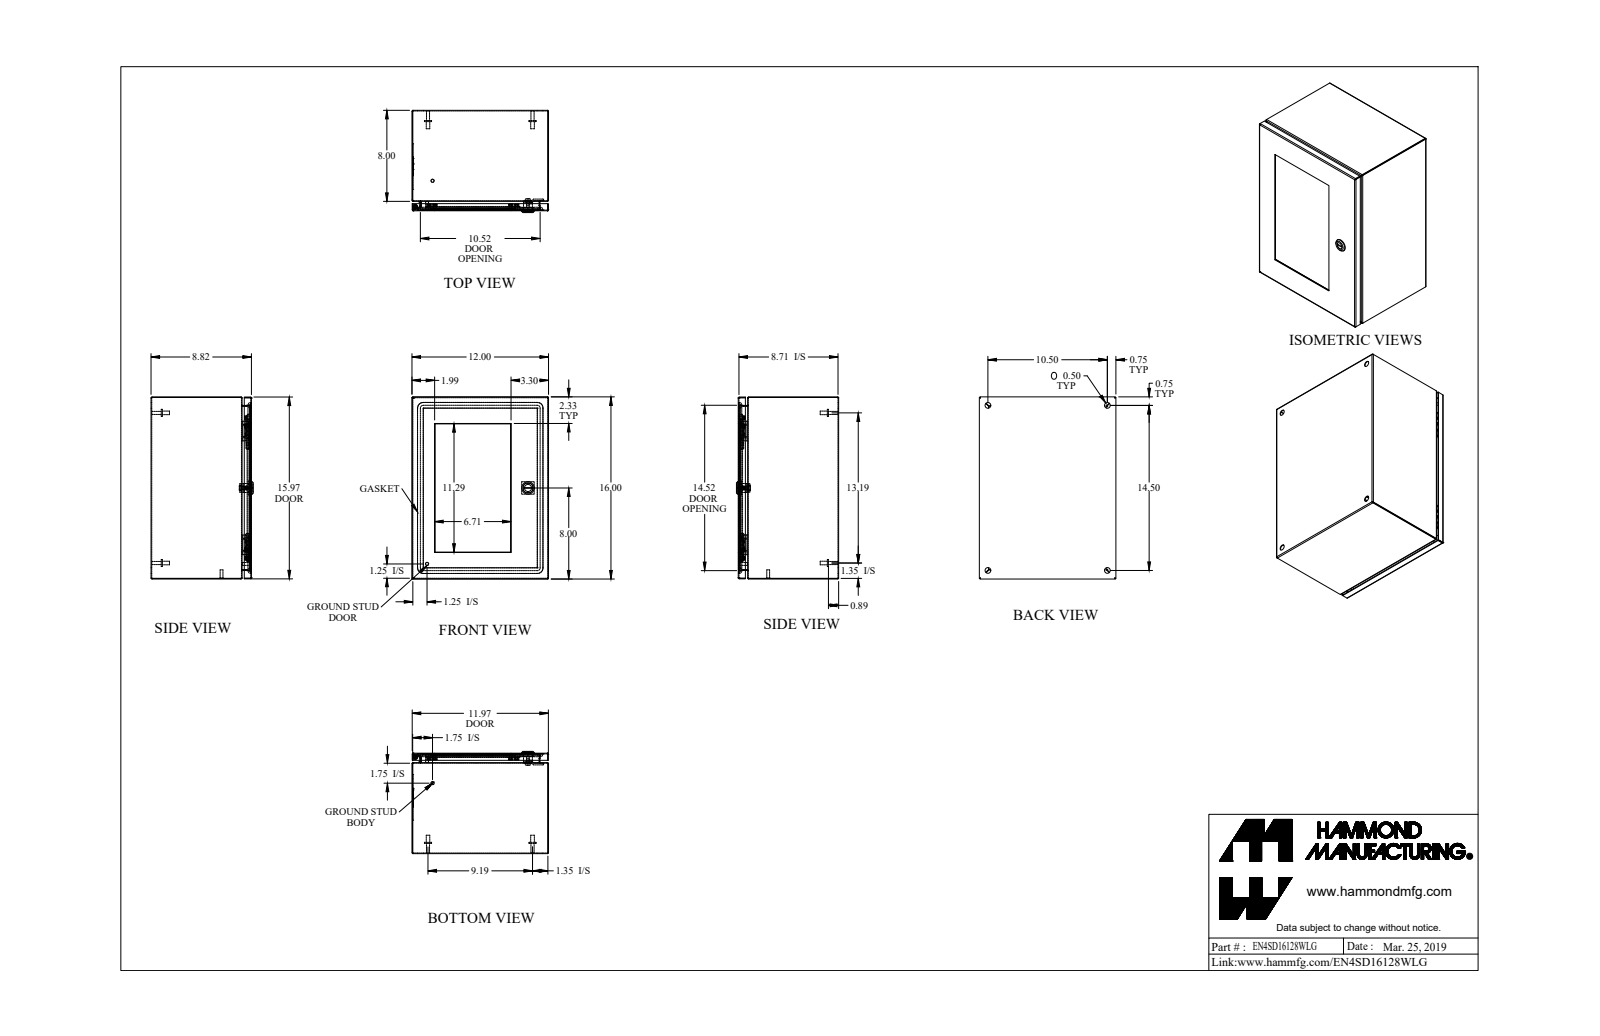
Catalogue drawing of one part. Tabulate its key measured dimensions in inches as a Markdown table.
| quantity | value |
| --- | --- |
| part name | EN4SD16128WLG_Default |
| STEP written by | SolidWorks 2019 (CONFIG_CONTROL_DESIGN) |
| units | inches |
| bodies | 50 solids, 1061 faces (526 planar, 329 cylindrical, 206 other) |
| overall size | 16 × 12 × 8.982 |
| volume | 79.9 in³ |
| surface area | 2 161 in² |
| round holes (diameter × count) | 0.13 × 10, 0.25 × 10, 0.5 × 4, 0.172 × 1, 0.232 × 1, 0.24 × 1, 0.242 × 1, 0.625 × 1, 0.785 × 1 |
| round bosses / shafts (diameter × count) | 0.226 × 11, 0.368 × 10, 0.164 × 10, 0.625 × 4, 0.313 × 4, 0.27 × 4, 0.281 × 2, 0.25 × 2 |
| partial cylindrical surfaces (radius × count) | 0.029 × 21, 0.086 × 21, 0.25 × 16, 0.125 × 10, 19 × 8, 0.006 × 4, 0.016 × 4, 0.062 × 4 |
| main face-to-face distances | 0.057, 8.765, 11.943, 8.708, 15.943, 11.886, 12, 0.25, 8.822, 0.307 |
| hole center spacings | 5.437, 5.438, 10.875, 11.617, 0.894, 0.895, 6.188, 6.189 |
